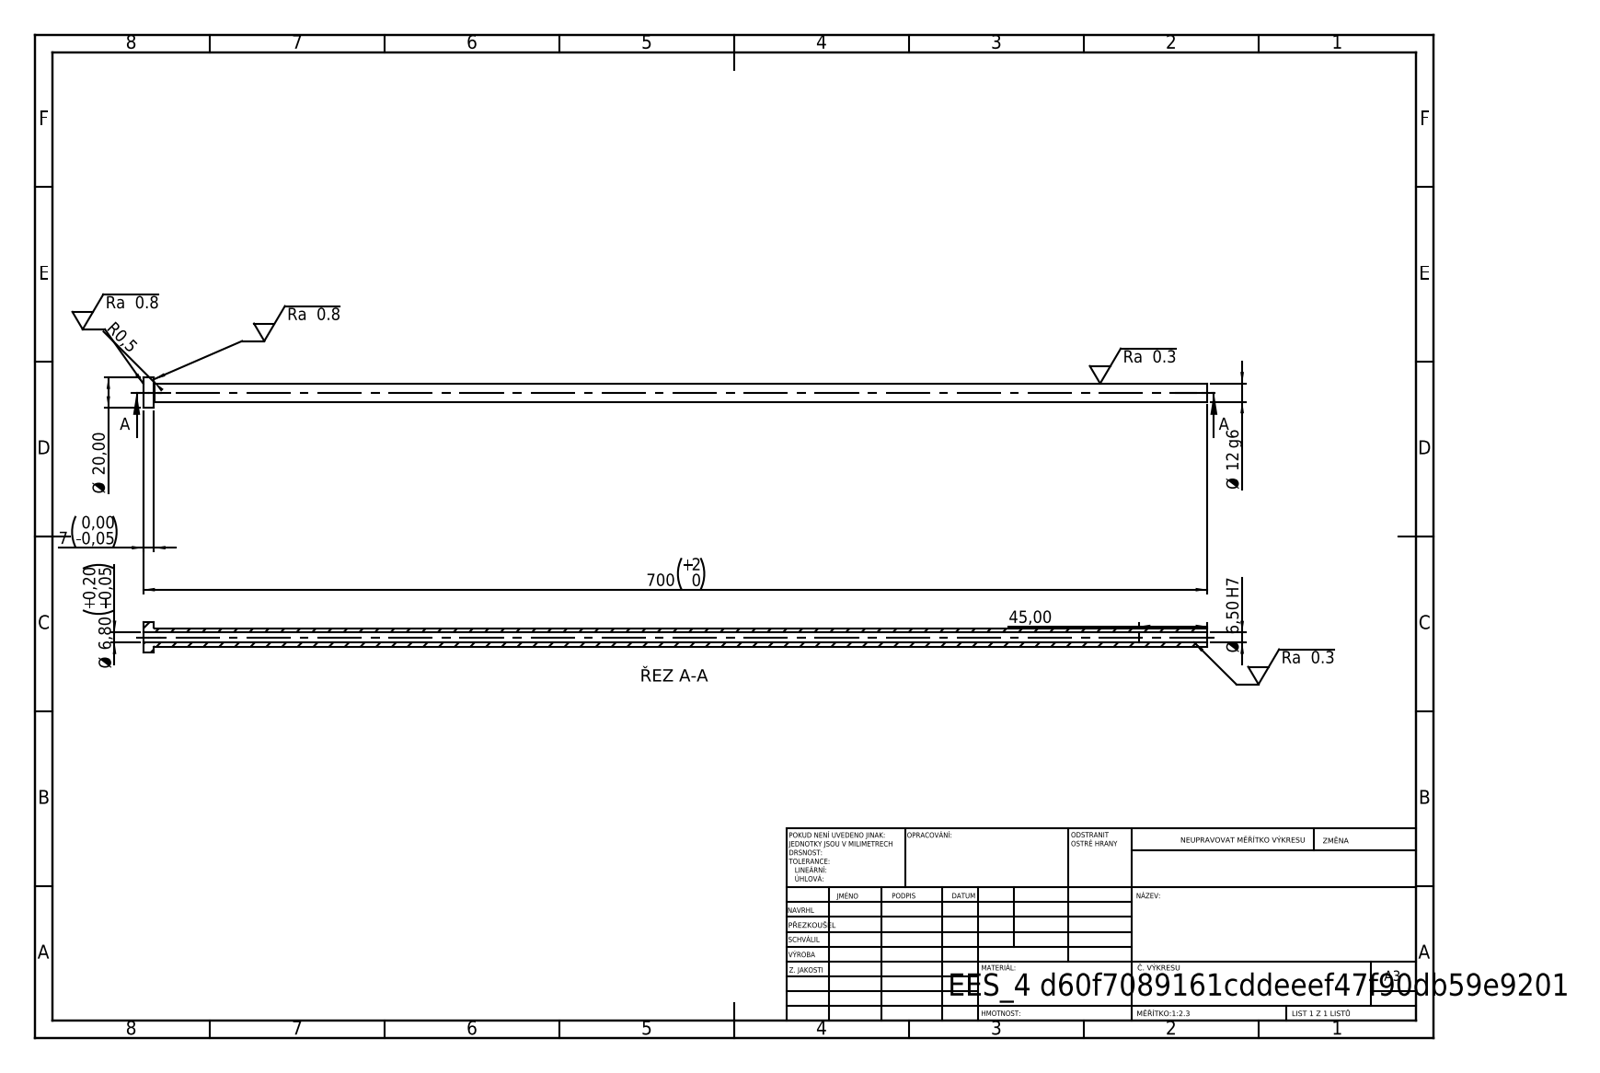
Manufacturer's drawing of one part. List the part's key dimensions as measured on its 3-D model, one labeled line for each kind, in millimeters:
STEP written by: SolidWorks 2019 (CONFIG_CONTROL_DESIGN)
Units: millimetres
Bodies: 1 solid, 14 faces (4 planar, 8 cylindrical, 2 other)
Overall size (bounding box): 700 × 20 × 20
Volume: 55 297 mm³ · Surface area: 42 031 mm²
Round holes (diameter × count): ⌀6.5 ×1, ⌀6.8 ×1
Round bosses / shafts (diameter × count): ⌀20 ×1, ⌀12 ×1
Main face-to-face distances: 7, 700, 693, 655, 648, 45
